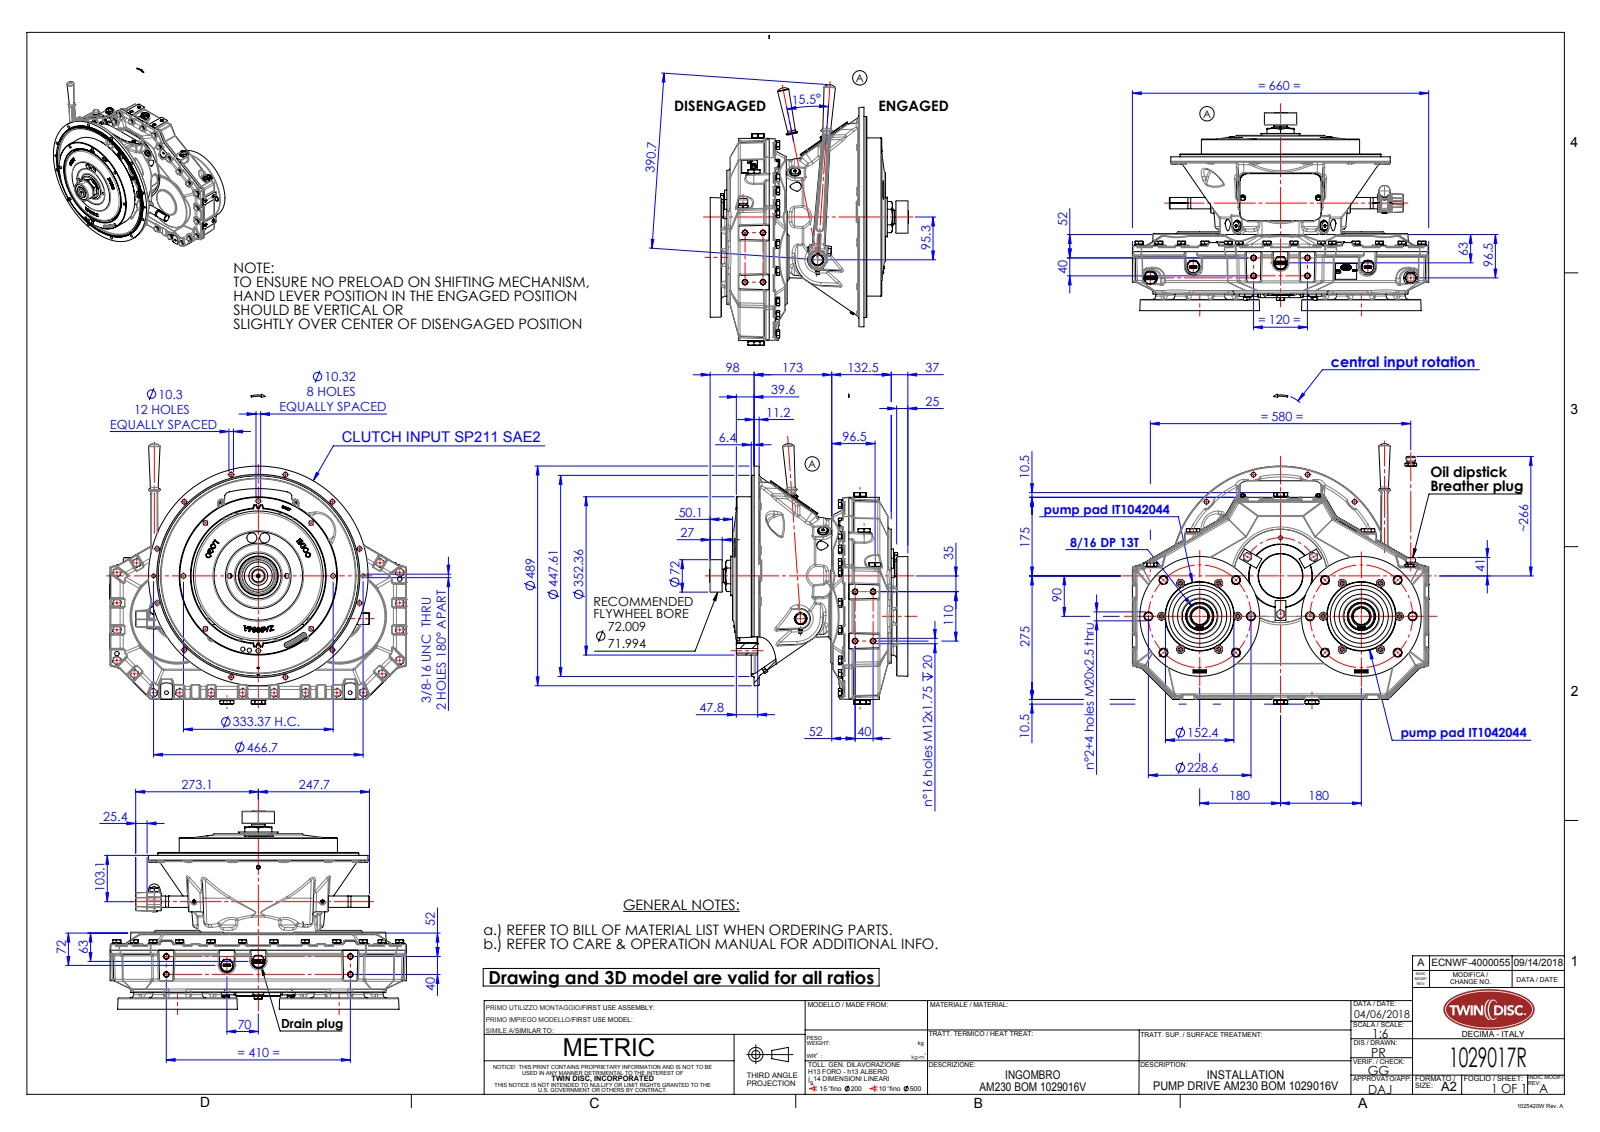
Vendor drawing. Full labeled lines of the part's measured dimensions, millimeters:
Part name (STEP PRODUCT): IT4588040_rev00-installation; PX1031738D; ITam230-002_rev00-installation; IT2021216_rev03-installation (+5 more)
STEP written by: SolidWorks 2015 (AUTOMOTIVE_DESIGN)
Units: millimetres
Bodies: 29 solids, 10114 faces (3361 planar, 2574 cylindrical, 4179 other)
Overall size (bounding box): 690.04 × 660 × 440.6
Volume: 3 730 000 mm³ · Surface area: 3 733 000 mm²
Round holes (diameter × count): ⌀10.2 ×40, ⌀10.5 ×40, ⌀8.5 ×30, ⌀12 ×20, ⌀11 ×15, ⌀10.3 ×12, ⌀17 ×12, ⌀17.5 ×12, ⌀10 ×10, ⌀30 ×9, ⌀10.32 ×8, ⌀13 ×6
Round bosses / shafts (diameter × count): ⌀10 ×45, ⌀16.2 ×33, ⌀18.1 ×32, ⌀20 ×13, ⌀16 ×12, ⌀140 ×3, ⌀98.7 ×3, ⌀82 ×3
Partial cylindrical surfaces — rounded edges, fillets, slot ends (radius × count): R0.1 ×224, R2 ×209, R3 ×133, R0.25 ×92, R5 ×80, R2.5 ×78, R0.35 ×70, R29.53 ×58
Main face-to-face distances: 21, 94.5, 37, 131.5, 25, 5, 19, 40, 152.5, 115.5
Hole centre spacings: 120, 57.4, 75, 138.58, 40, 207.84, 22.59, 51.37
